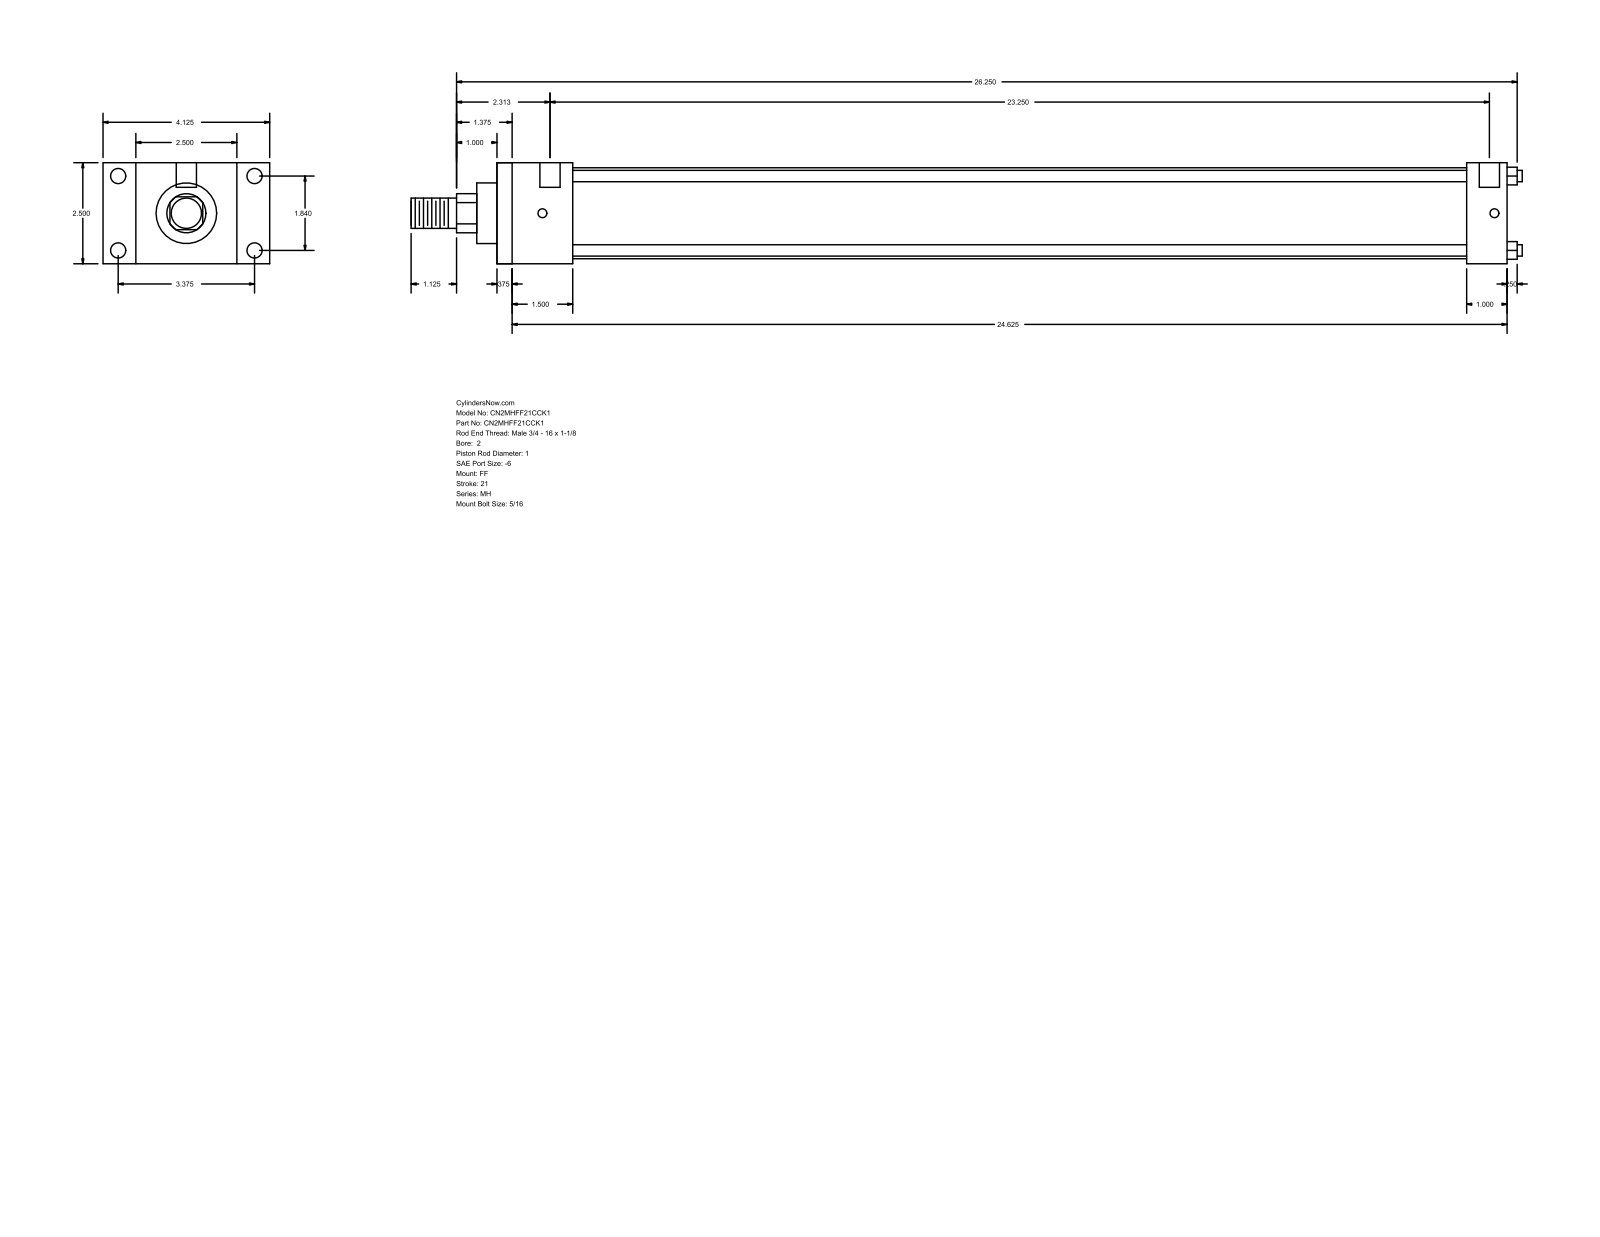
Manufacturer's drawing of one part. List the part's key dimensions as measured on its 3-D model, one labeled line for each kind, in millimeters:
Part name (STEP PRODUCT): MH_FF__0200_1
STEP written by: GSSL Pune (CONFIG_CONTROL_DESIGN)
Units: millimetres
Bodies: 0 solids, 92 faces (64 planar, 28 cylindrical, 0 other)
Overall size (bounding box): 698.5 × 104.78 × 63.5
Round holes (diameter × count): ⌀5.56 ×4, ⌀9.53 ×4, ⌀12.7 ×2
Round bosses / shafts (diameter × count): ⌀7.14 ×4, ⌀57.15 ×1, ⌀38.1 ×1, ⌀25.4 ×1, ⌀19.05 ×1
Partial cylindrical surfaces — rounded edges, fillets, slot ends (radius × count): R12.29 ×1
Main face-to-face distances: 63.5, 635, 9.52, 625.48, 20.64, 25.4, 47.63, 609.6, 38.11, 600.08
Hole centre spacings: 46.74, 85.72, 97.63, 598.48, 3.17, 4.76, 590.55, 593.72
